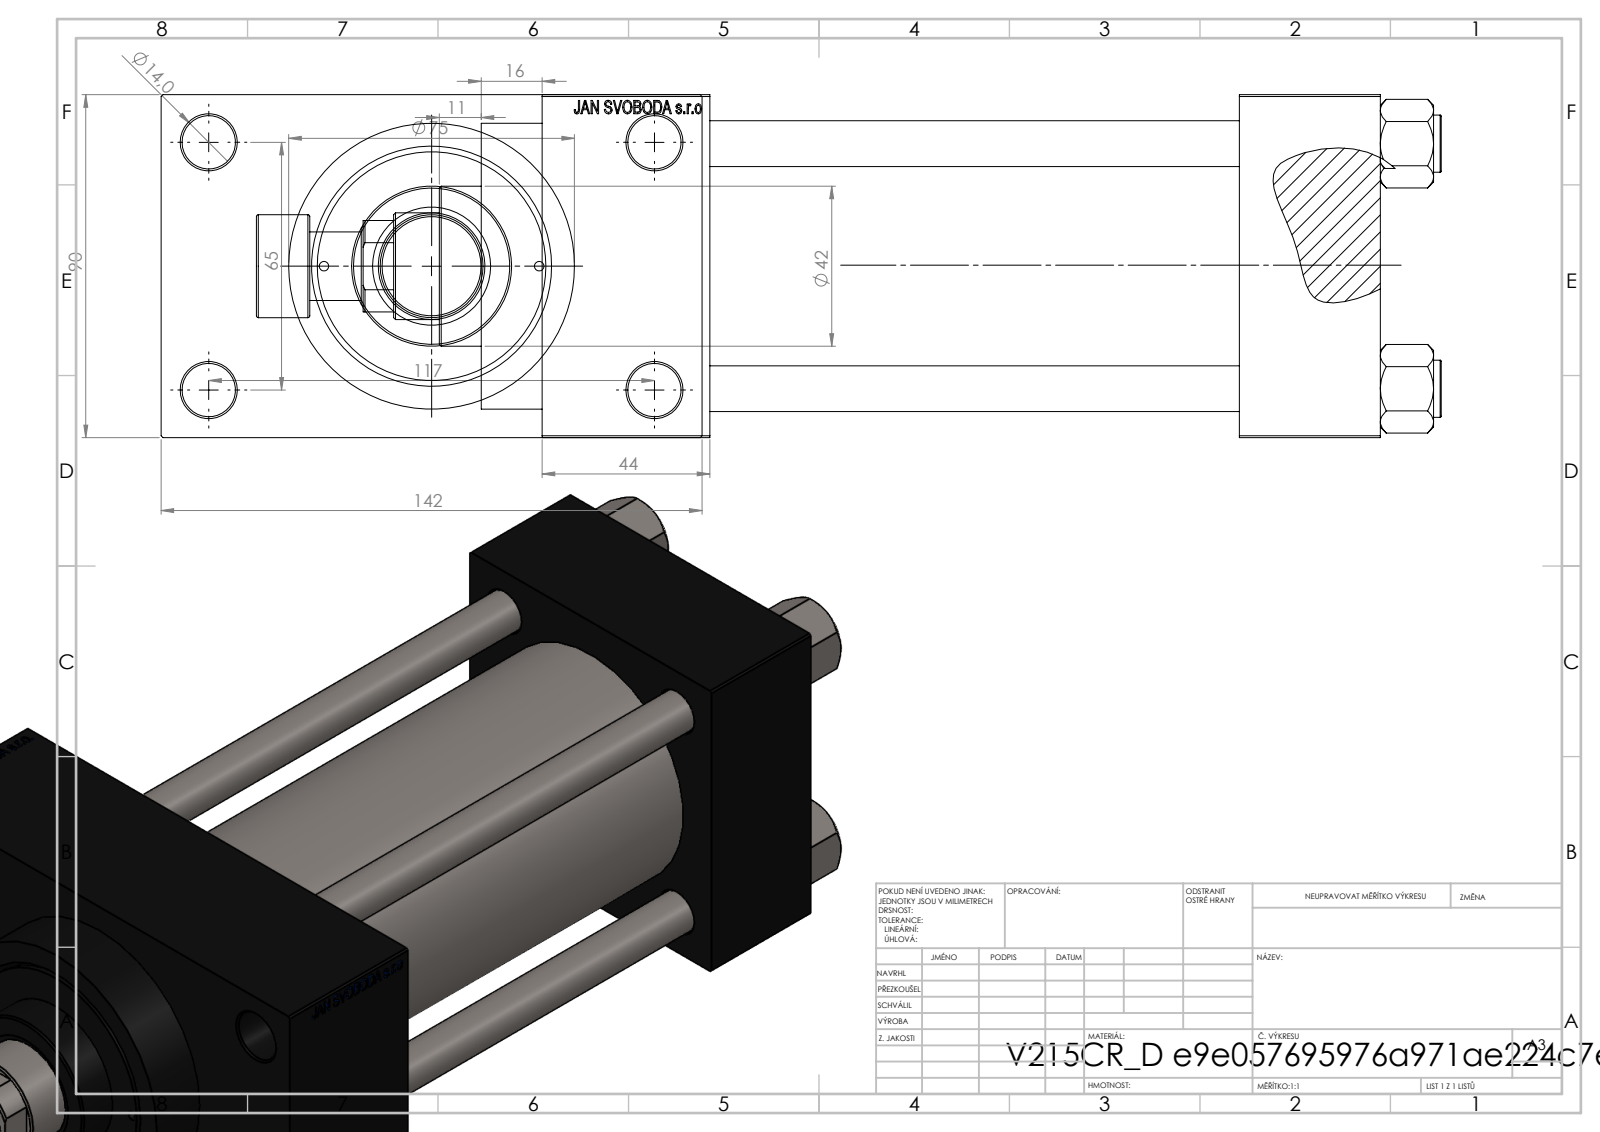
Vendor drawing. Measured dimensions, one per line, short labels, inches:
name: NUT_M5_D; V215_VC_A; V215CR_D_Body; V215CR_ROD_END_F (+2 more)
written by: SolidWorks 2019 (CONFIG_CONTROL_DESIGN)
unit: in
bodies: 11 solids, 1127 faces (504 planar, 97 cylindrical, 526 other)
size: 12.244 × 5.591 × 3.543
volume: 27.49 in³; area: 364.7 in²
holes: 4× ⌀0.472, 4× ⌀0.551, 2× ⌀0.098, 2× ⌀0.276, 2× ⌀0.825, 2× ⌀1.181, 1× ⌀0.728, 1× ⌀1.102, 1× ⌀1.22, 1× ⌀1.969, 1× ⌀2.362, 1× ⌀2.48
bosses: 4× ⌀0.591, 1× ⌀2.953, 1× ⌀2.717, 1× ⌀1.654, 1× ⌀1.063, 1× ⌀0.709
face distances: 7.205, 1.732, 5.472, 1.457, 6.929, 8.661, 1.024, 4.567, 3.543, 5.591
hole spacings: 1.037, 1.275, 1.748, 1.79, 2.531, 2.635, 2.694, 2.748
